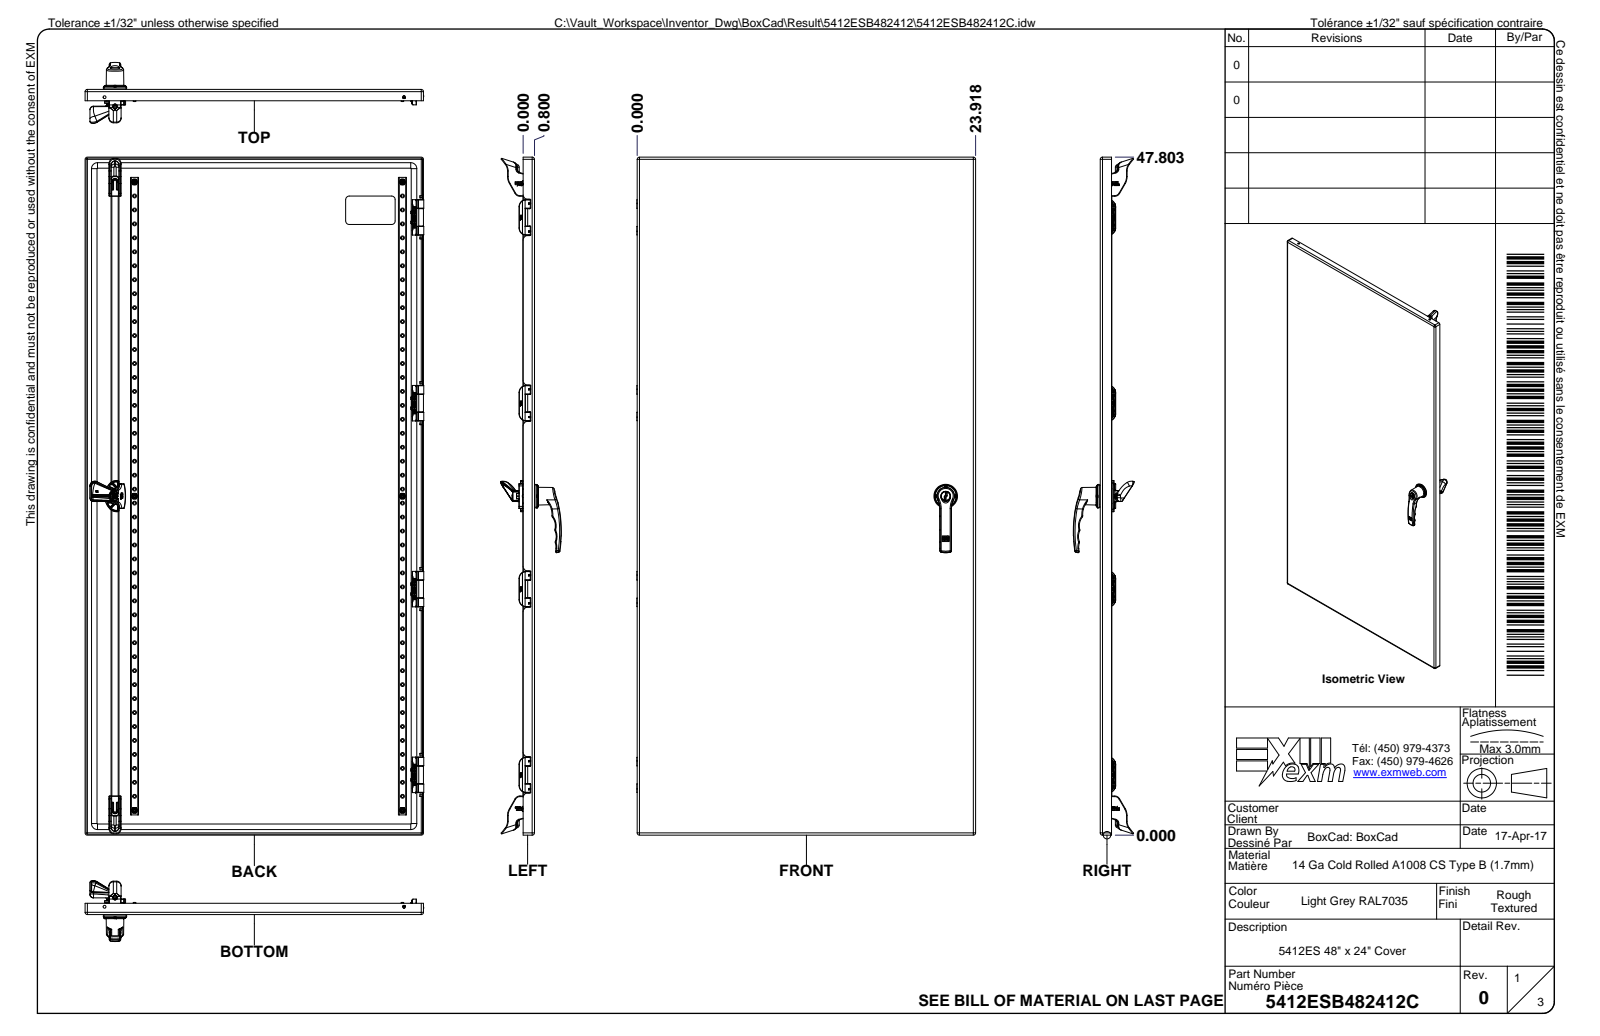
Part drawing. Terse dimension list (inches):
name: 5412ESB482412; 5412ESB482412B; 5412ESB482412B-P; STK-Q-16005 (+8 more)
written by: Autodesk Inventor 2024 (AUTOMOTIVE_DESIGN)
unit: in
bodies: 98 solids, 16529 faces (4176 planar, 4278 cylindrical, 8075 other)
size: 48 × 24.018 × 14.985
volume: 439.1 in³; area: 11 692 in²
holes: 88× ⌀0.165, 16× ⌀0.043, 15× ⌀0.03, 12× ⌀0.315, 11× ⌀0.201, 9× ⌀0.311, 8× ⌀0.178, 6× ⌀0.197, 6× ⌀0.268, 6× ⌀0.27, 4× ⌀0.187, 4× ⌀0.22
bosses: 88× ⌀0.237, 16× ⌀0.039, 15× ⌀0.03, 12× ⌀0.232, 6× ⌀0.717, 6× ⌀0.472, 6× ⌀0.374, 6× ⌀0.311
rounds: 310× R0.02, 267× R0.039, 266× R0.01, 136× R0.008, 58× R0.016, 56× R0.079, 42× R0.059, 36× R0.004
face distances: 0.068, 13.052, 12.983, 23.932, 13.12, 0.942, 0.874, 12.109, 12.178, 1.047
hole spacings: 13.101, 26.202, 1.969, 0.35, 0.735, 1.052, 1.385, 13.101
